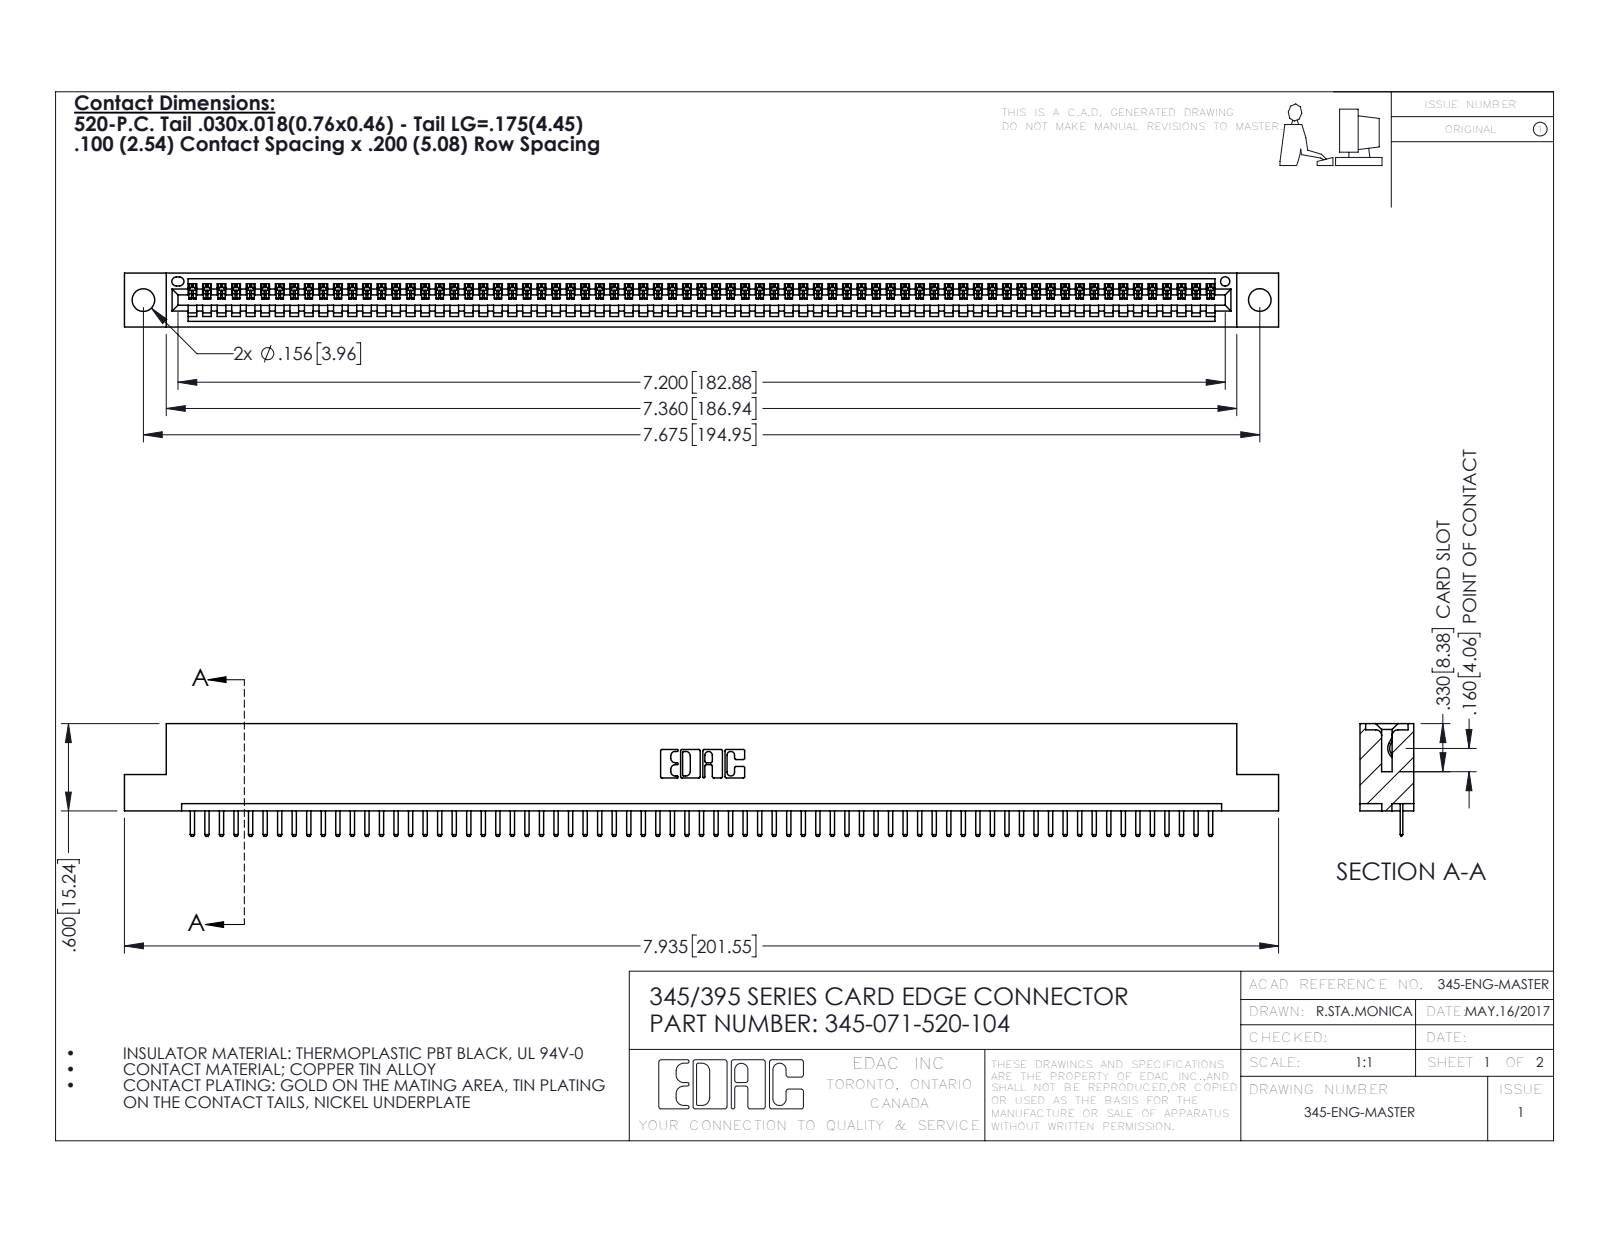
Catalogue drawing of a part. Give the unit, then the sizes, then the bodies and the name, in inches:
Units: inches
Overall size (bounding box): 7.935 × 0.775 × 0.37
Round holes (diameter × count): ⌀0.156 ×2, ⌀0.064 ×1
Partial cylindrical surfaces — rounded edges, fillets, slot ends (radius × count): R0.01 ×144, R0.006 ×142, R0.01 ×22, R0.007 ×6, R0.031 ×6, R0.026 ×3, R0.031 ×2, R0.04 ×2
Main face-to-face distances: 0.298, 0.072, 0.37, 0.2, 0.098, 0.272, 0.025, 0.225, 0.072, 0.149
Hole centre spacings: 0.27, 7.439, 7.675
Volume: 1.165 in³ · Surface area: 38.6 in²
Bodies: 72 solids, 4528 faces (3062 planar, 1466 cylindrical, 0 other)
Part name (STEP PRODUCT): 345-071-520-104; 345-292-001_345-293-120; 345 Part_Flush Mounting Lugs - 0.156 Dia-TH
STEP written by: SolidWorks 2016 (CONFIG_CONTROL_DESIGN)
